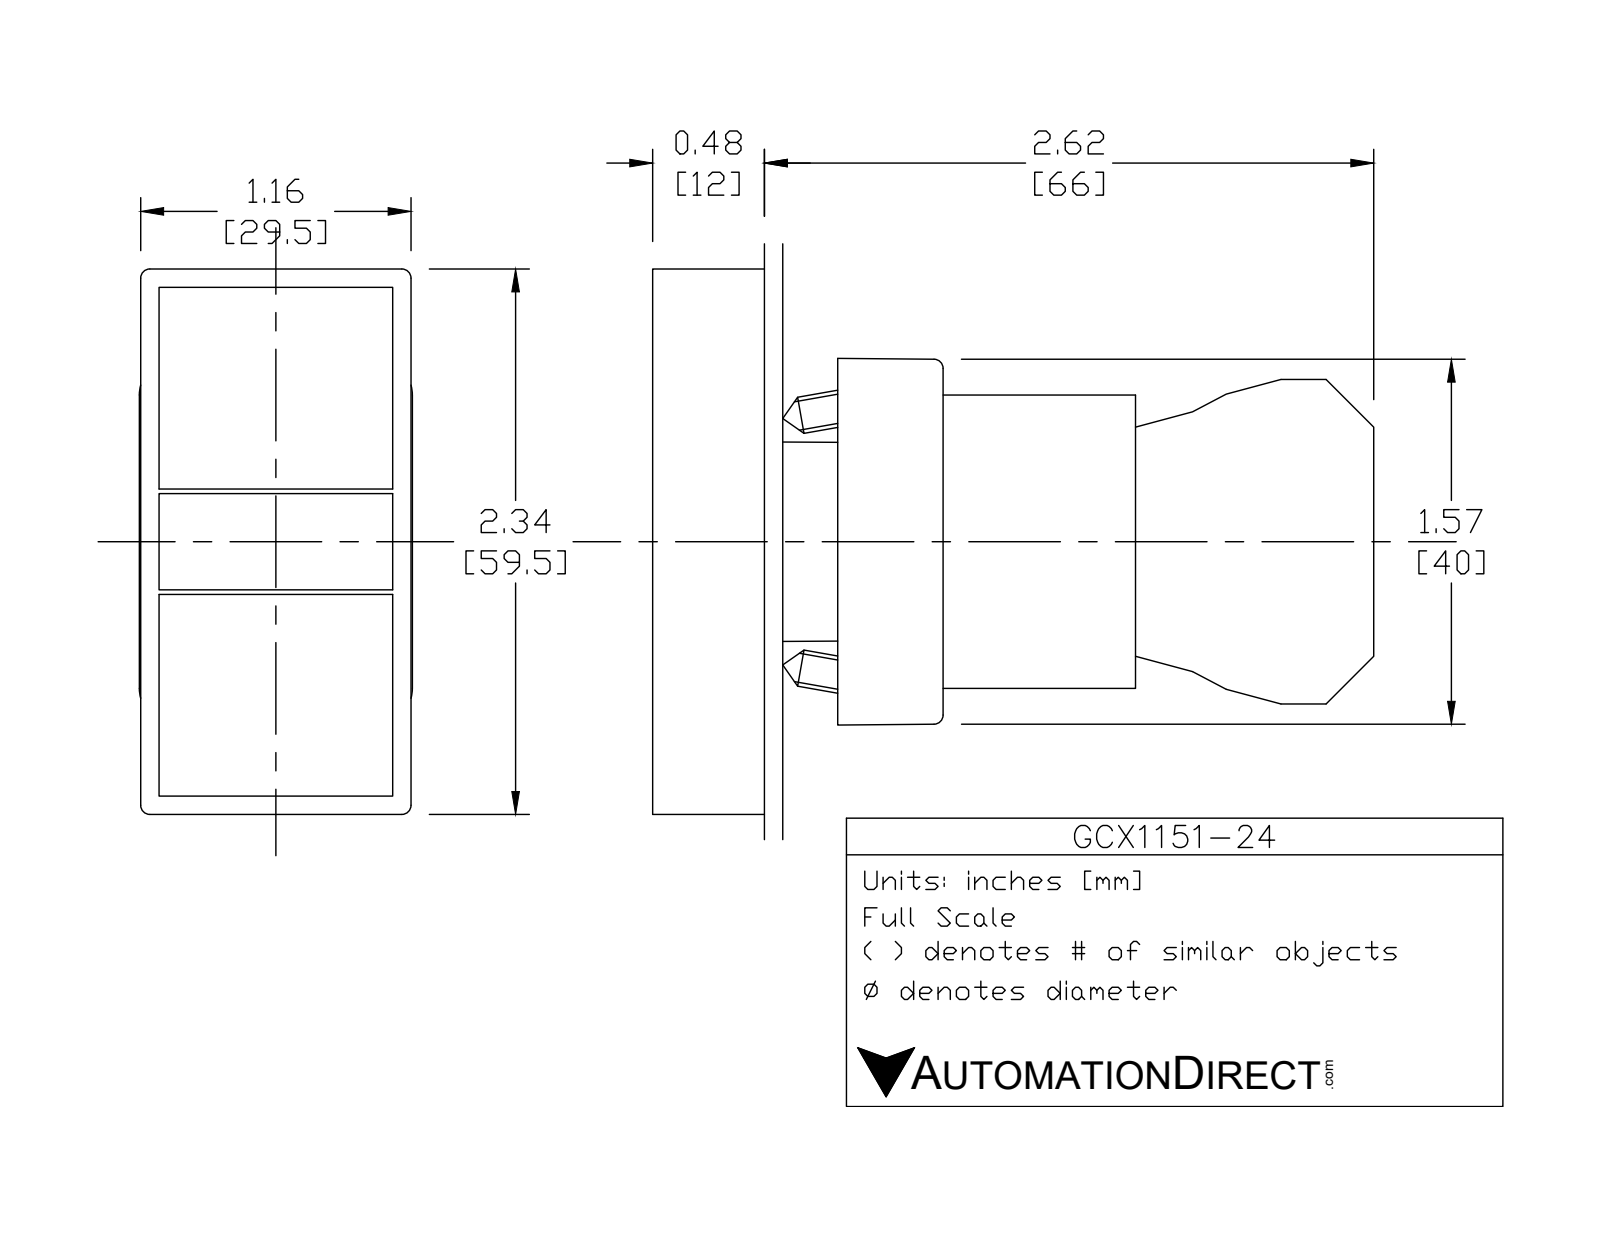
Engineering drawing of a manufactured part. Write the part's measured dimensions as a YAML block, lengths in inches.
part_name: "GCX1151-24; ecx1040; GCX1151-24 OPERATOR; ECX1050 (+2 more)"
step_written_by: "SolidWorks 2016 (AUTOMOTIVE_DESIGN)"
units: inches
bodies: {solids: 9, faces: 531, planar: 348, cylindrical: 152, other: 31}
overall_size: [3.043, 2.343, 1.177]
volume: 4.281
surface_area: 55.77
round_holes:
  - {diameter: 0.079, count: 4}
  - {diameter: 0.087, count: 2}
  - {diameter: 0.124, count: 2}
  - {diameter: 0.13, count: 2}
  - {diameter: 0.197, count: 1}
  - {diameter: 0.469, count: 1}
  - {diameter: 0.878, count: 1}
  - {diameter: 0.888, count: 1}
round_bosses_or_shafts:
  - {diameter: 0.157, count: 4}
  - {diameter: 0.945, count: 1}
  - {diameter: 0.856, count: 1}
  - {diameter: 0.78, count: 1}
  - {diameter: 0.504, count: 1}
partial_cylinders:
  - {radius: 0.059, count: 24}
  - {radius: 0.041, count: 12}
  - {radius: 0.124, count: 12}
  - {radius: 0.157, count: 12}
  - {radius: 0.039, count: 8}
  - {radius: 0.063, count: 2}
  - {radius: 0.079, count: 2}
  - {radius: 0.128, count: 2}
face_to_face_distances: [0.039, 0.059, 0.02, 0.453, 0.579, 0.593, 0.74, 1.193, 0.827, 1.567]
hole_center_spacings: [0.236, 1.003, 0.974, 0.472, 0.539, 0.544, 1.083, 0.484]
